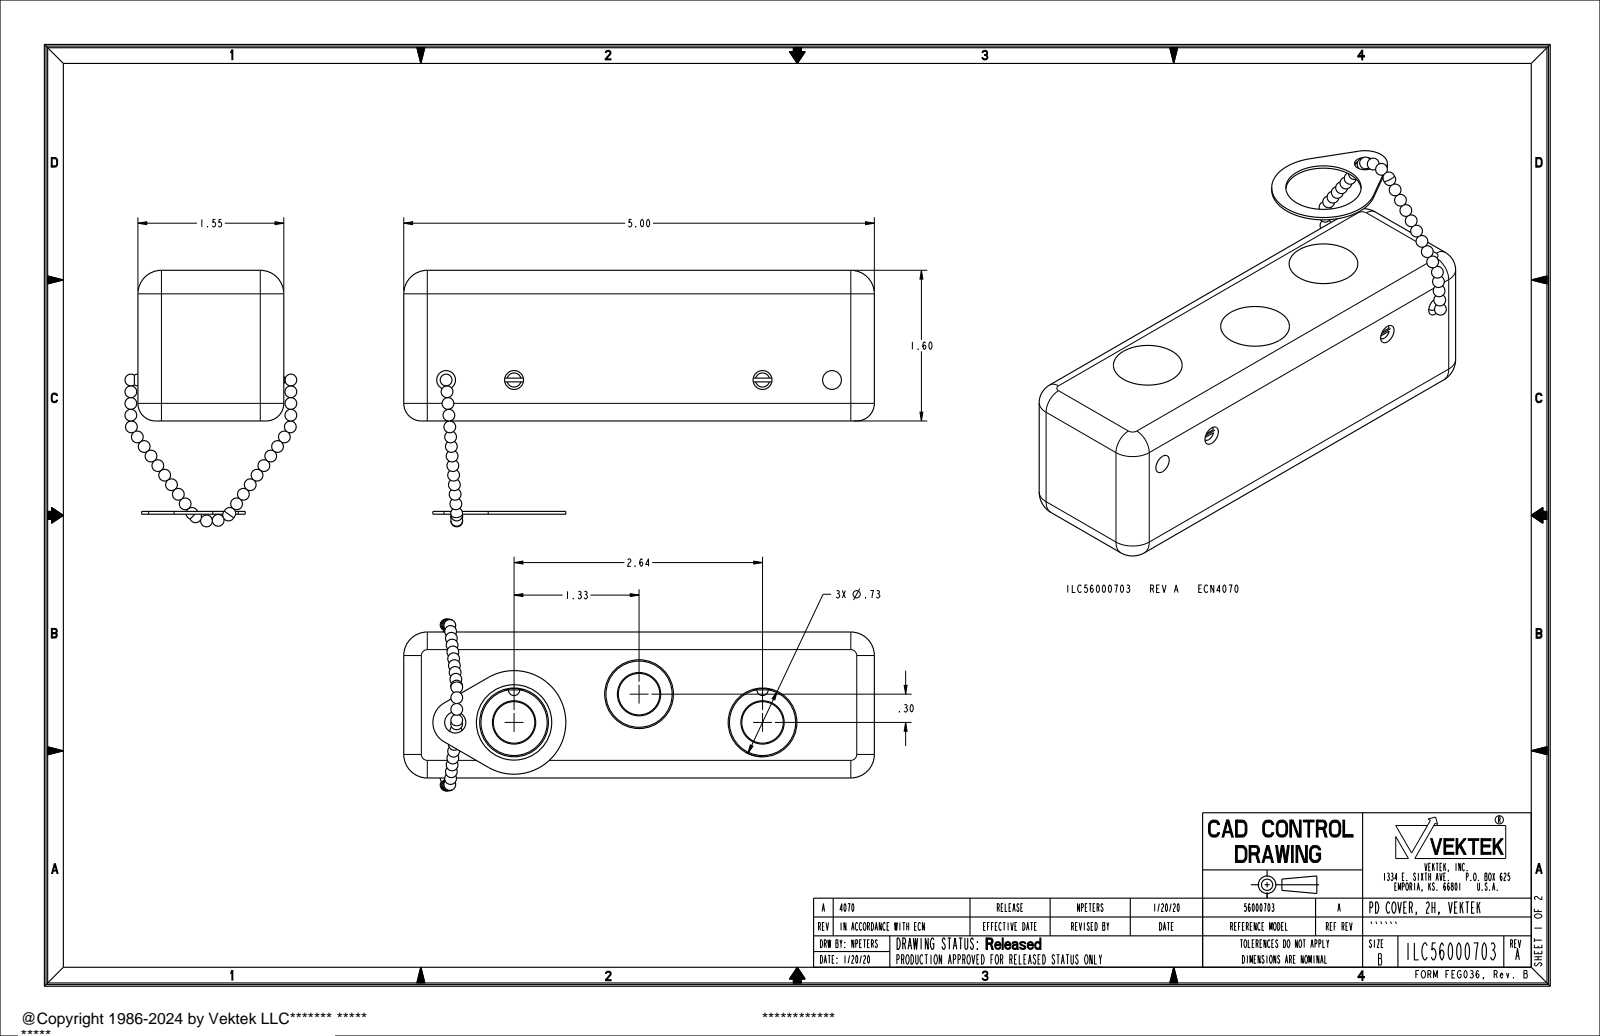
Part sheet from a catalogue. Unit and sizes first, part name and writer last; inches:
Units: inches
Overall size (bounding box): 5 × 2.724 × 1.825
Round holes (diameter × count): ⌀0.2 ×2, ⌀0.201 ×2, ⌀0.225 ×1, ⌀0.8 ×1
Round bosses / shafts (diameter × count): ⌀0.12 ×2
Partial cylindrical surfaces — rounded edges, fillets, slot ends (radius × count): R0.25 ×8, R0.187 ×4, R0.237 ×1, R0.55 ×1
Main face-to-face distances: 1.55, 1.6, 5, 0.84, 0.76, 2.56, 1.72, 0.96, 2.59, 1.75
Hole centre spacings: 0.625, 0.722, 0.738, 2.64, 3.362, 3.378, 4.1
Bodies: 0 solids, 208 faces (24 planar, 30 cylindrical, 154 other)
Part name (STEP PRODUCT): ILC56000703
STEP written by: PRO/ENGINEER BY PARAMETRIC TECHNOLOGY CORPORATION, 2013320 (AUTOMOTIVE_DESIGN)
